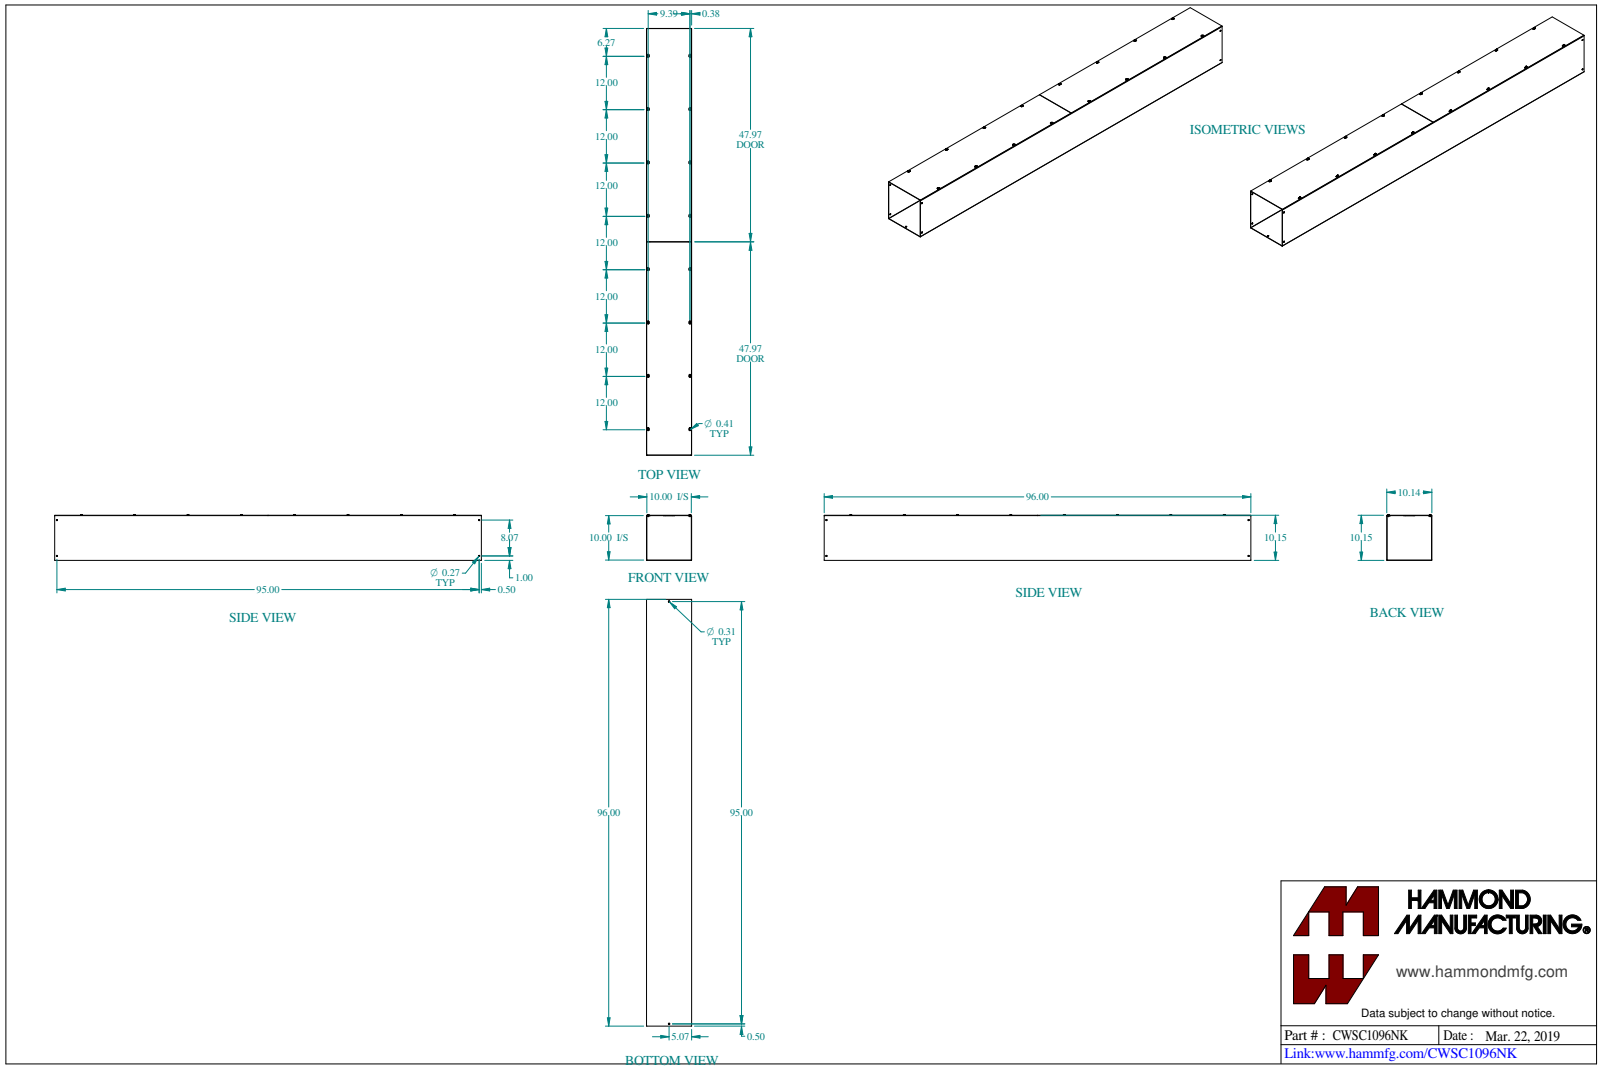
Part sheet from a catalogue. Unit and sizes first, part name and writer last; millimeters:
Units: millimetres
Overall size (bounding box): 2438.4 × 262.3 × 257.7
Round holes (diameter × count): ⌀4.5 ×16, ⌀6.8 ×4, ⌀8 ×2
Round bosses / shafts (diameter × count): ⌀9.5 ×16, ⌀4.8 ×16
Partial cylindrical surfaces — rounded edges, fillets, slot ends (radius × count): R3.2 ×16, R5.2 ×16, R0.9 ×4, R2.7 ×4
Main face-to-face distances: 1.8, 255.8, 254, 2, 257.8, 256, 257.7, 252.2, 3.8, 0.8
Hole centre spacings: 304.8, 387.1, 609.6, 654.6, 914.4, 945, 238.6, 1219.2
Volume: 4 788 000 mm³ · Surface area: 5 158 000 mm²
Bodies: 19 solids, 558 faces (274 planar, 188 cylindrical, 96 other)
Part name (STEP PRODUCT): CWSC1096NK
STEP written by: SolidWorks 2023 (CONFIG_CONTROL_DESIGN)
